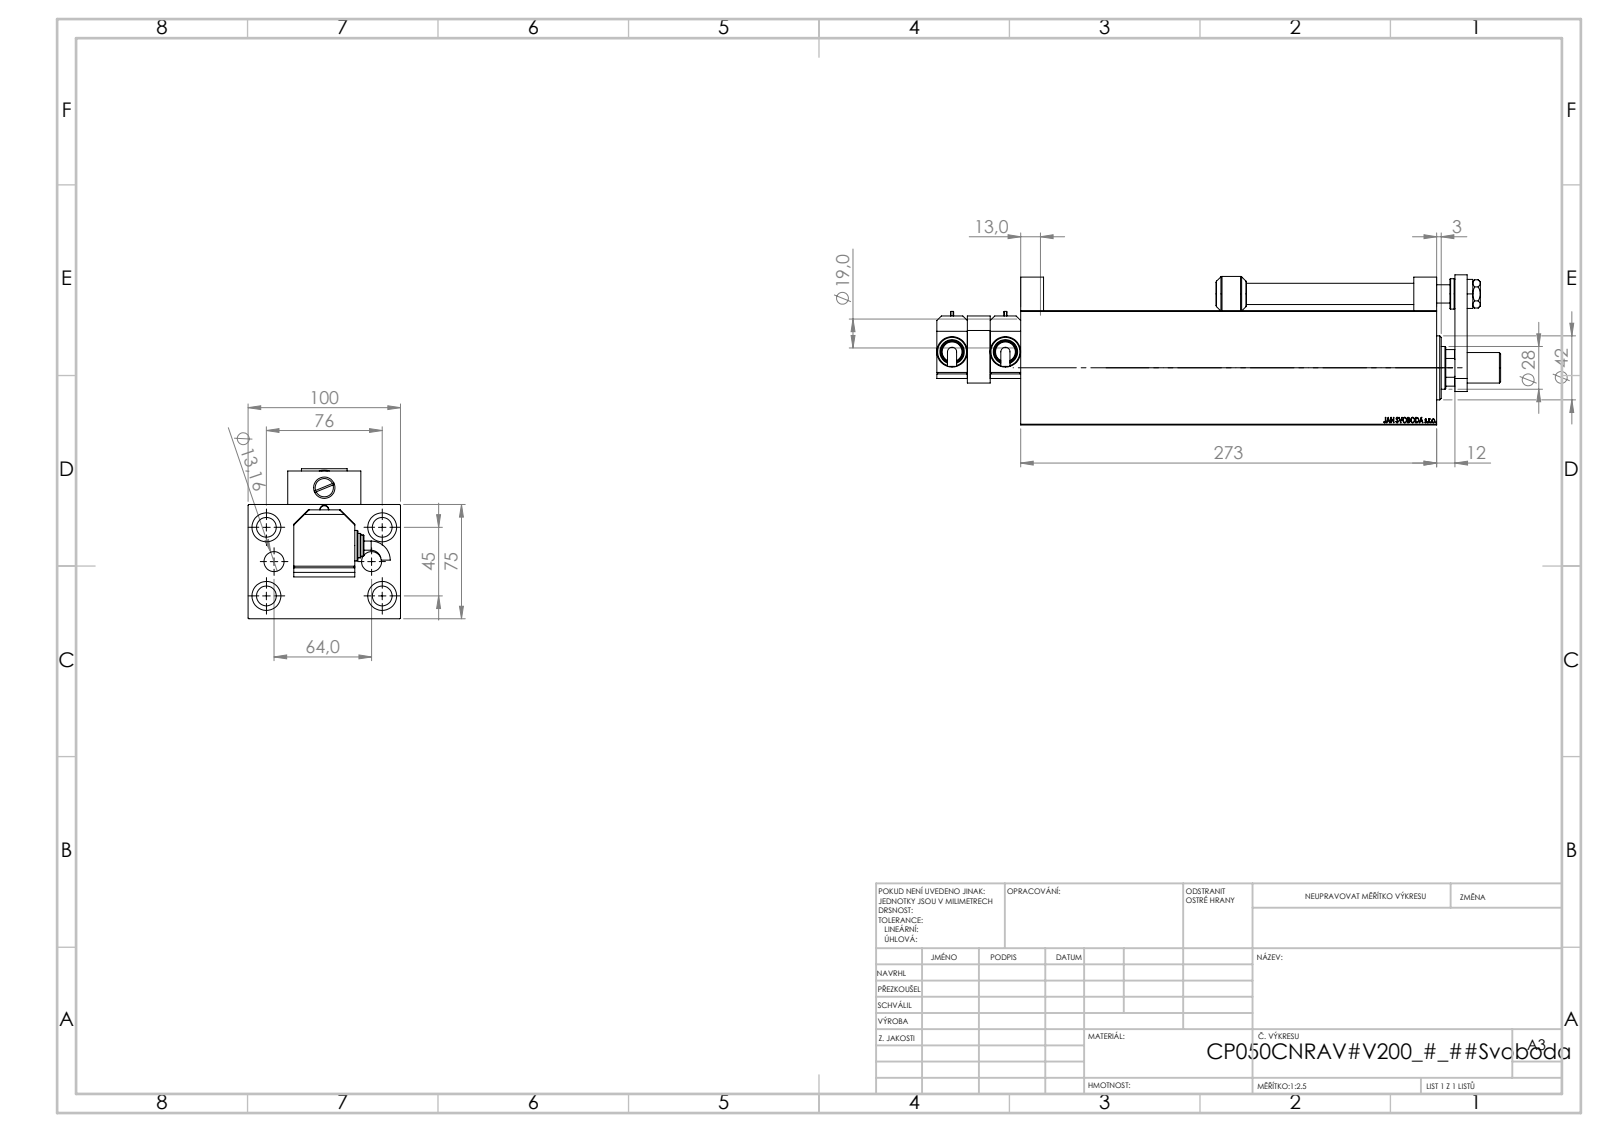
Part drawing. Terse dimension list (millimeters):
name: NUT_D16; V450CM_VC_B; V450CM_C_Body; TYC_P (+7 more)
written by: SolidWorks 2019 (CONFIG_CONTROL_DESIGN)
unit: mm
bodies: 15 solids, 1094 faces (523 planar, 116 cylindrical, 455 other)
size: 370 × 100 × 98.5
volume: 1 787 000 mm³; area: 288 231 mm²
holes: 5× ⌀13, 4× ⌀4, 4× ⌀8, 4× ⌀19, 2× ⌀13.16, 1× ⌀12, 1× ⌀14, 1× ⌀16.5, 1× ⌀18.5, 1× ⌀28, 1× ⌀31.5, 1× ⌀50
bosses: 4× ⌀20, 2× ⌀16, 2× ⌀14, 2× ⌀6, 1× ⌀42, 1× ⌀23, 1× ⌀18
rounds: 1× R3, 1× R13.5
face distances: 75, 100, 35, 20, 293, 273, 15, 12, 14, 259
hole spacings: 44.16, 20, 23.05, 23.56, 45, 46.04, 72.58, 74.48
